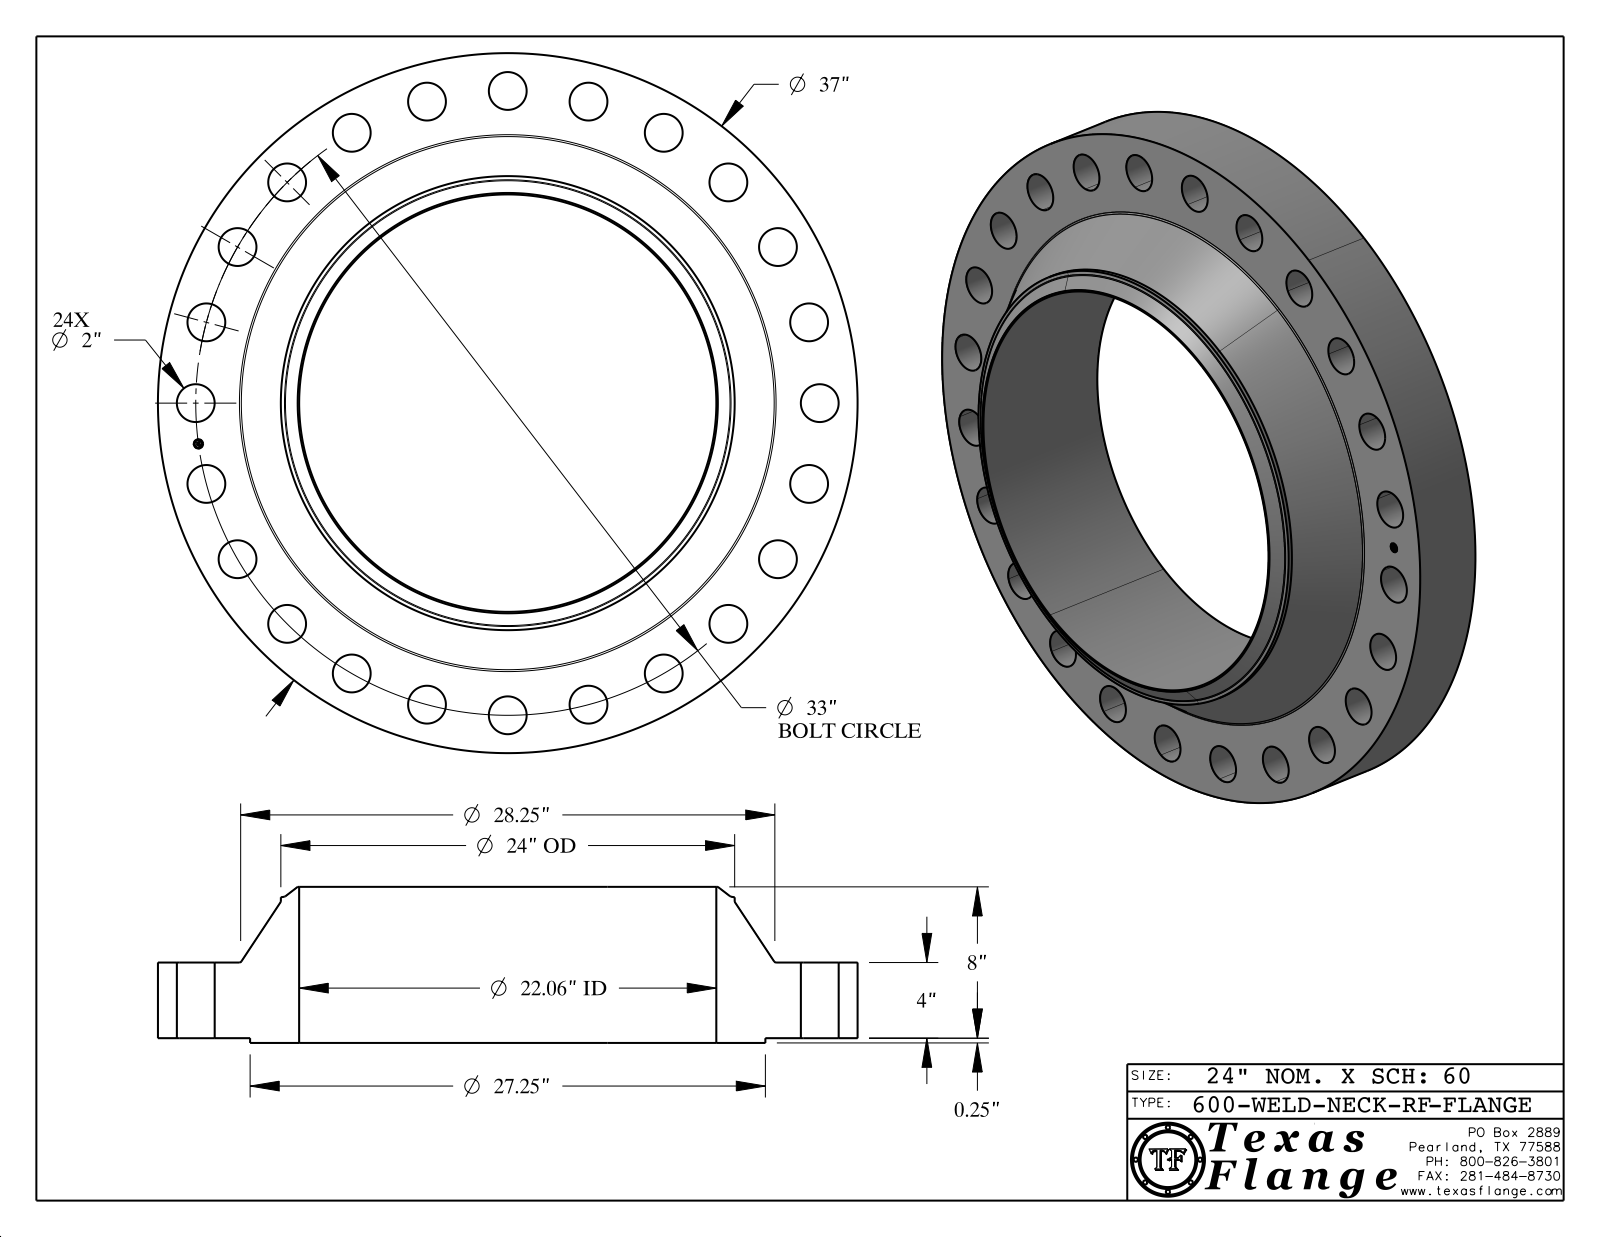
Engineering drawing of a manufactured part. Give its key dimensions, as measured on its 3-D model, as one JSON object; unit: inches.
{"part_name": "600-WELD-NECK-RF", "step_written_by": "CATIA V5 STEP AP214 (AUTOMOTIVE_DESIGN)", "units": "inches", "bodies": {"solids": 1, "faces": 455, "planar": 369, "cylindrical": 76, "other": 10}, "overall_size": [37, 37, 8.25], "volume_in3": 3052, "surface_area_in2": 3068, "round_holes": [[2, 24], [0.495, 1], [22.062, 1]], "round_bosses_or_shafts": [[0.03, 8], [37, 1], [27.25, 1], [24, 1], [0.39, 1]], "face_to_face_distances": [4, 0.25, 4.25, 8.25, 8, 0.015, 4.235, 3.985, 4.015, 0.07], "hole_center_spacings": [16.5, 4.307, 8.541, 20.089, 23.335, 26.181, 31.876, 32.718]}
